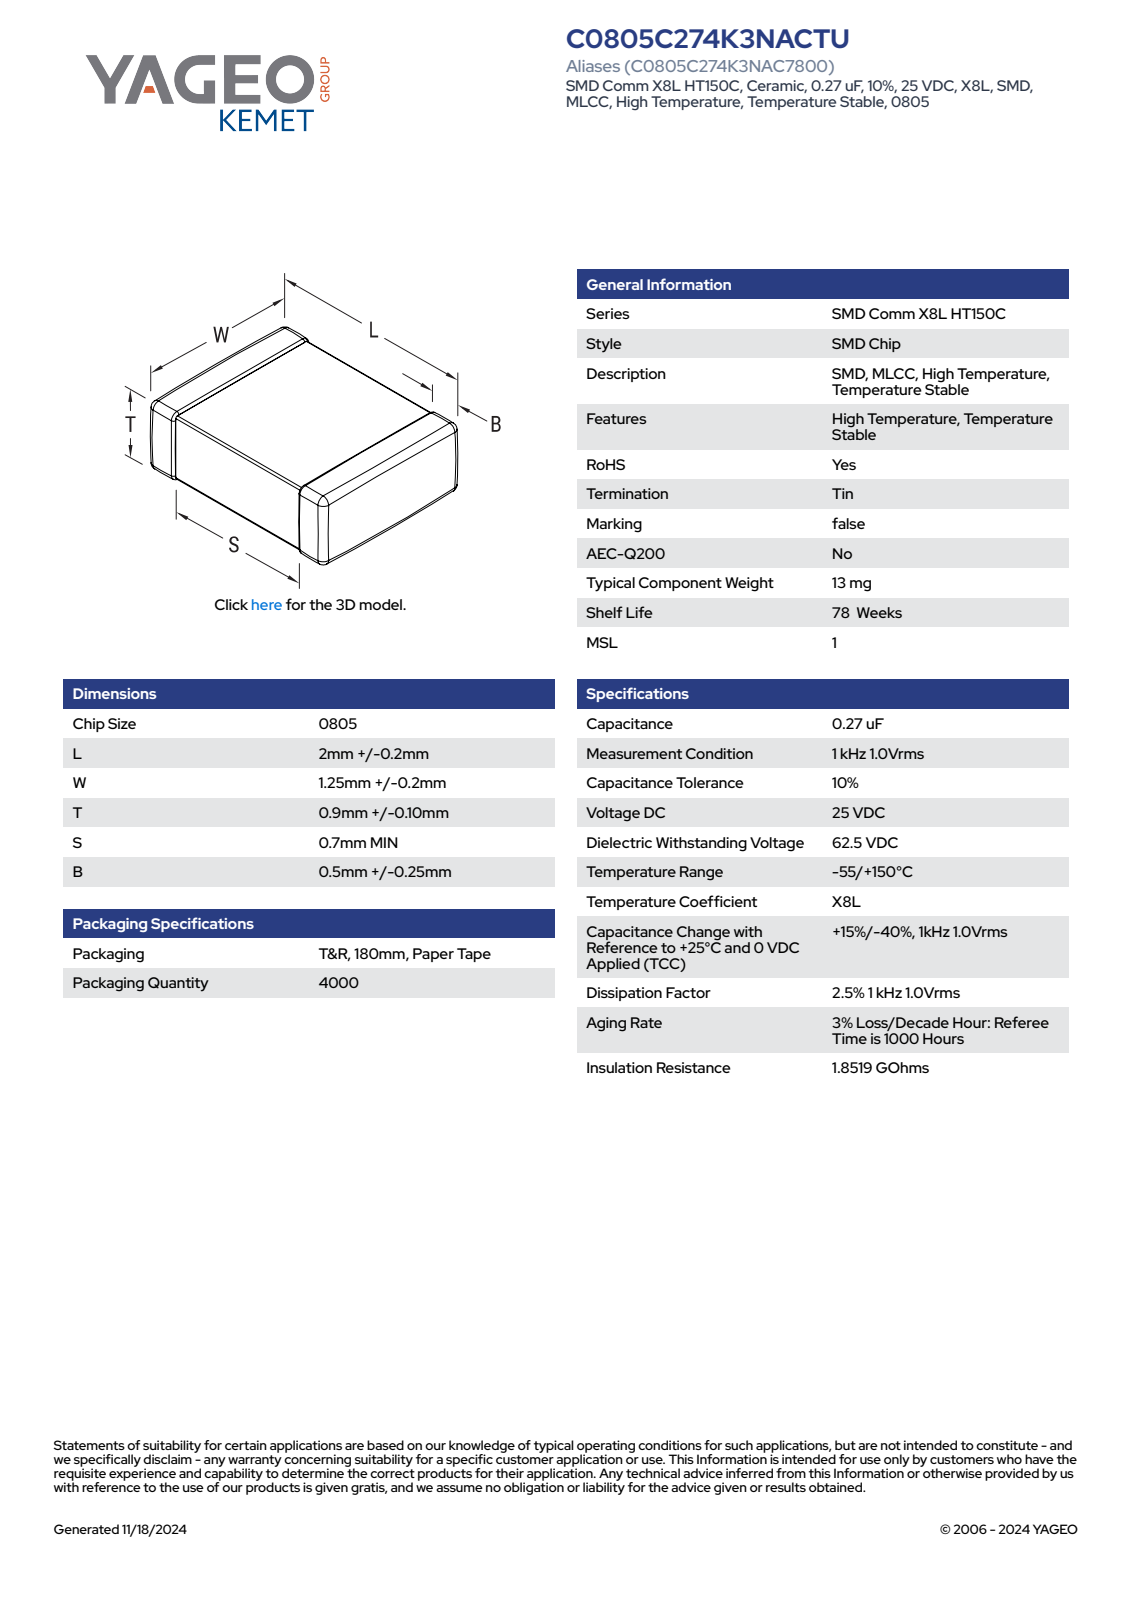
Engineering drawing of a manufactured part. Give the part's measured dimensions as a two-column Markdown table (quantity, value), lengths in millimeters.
| quantity | value |
| --- | --- |
| part name | CCS_CCSTD_0805_L2.2W1.45S1.25T1B0.5 |
| STEP written by | SolidWorks 2021 (AUTOMOTIVE_DESIGN) |
| units | millimeters |
| bodies | 4 solids, 121 faces (71 planar, 34 cylindrical, 16 other) |
| overall size | 2.2 × 1.45 × 1 |
| volume | 3 mm³ |
| surface area | 14 mm² |
| main face-to-face distances | 0.97, 1, 2.2, 1.45, 1.42, 0.94, 1.39, 1.23, 1.19, 1.01 |
